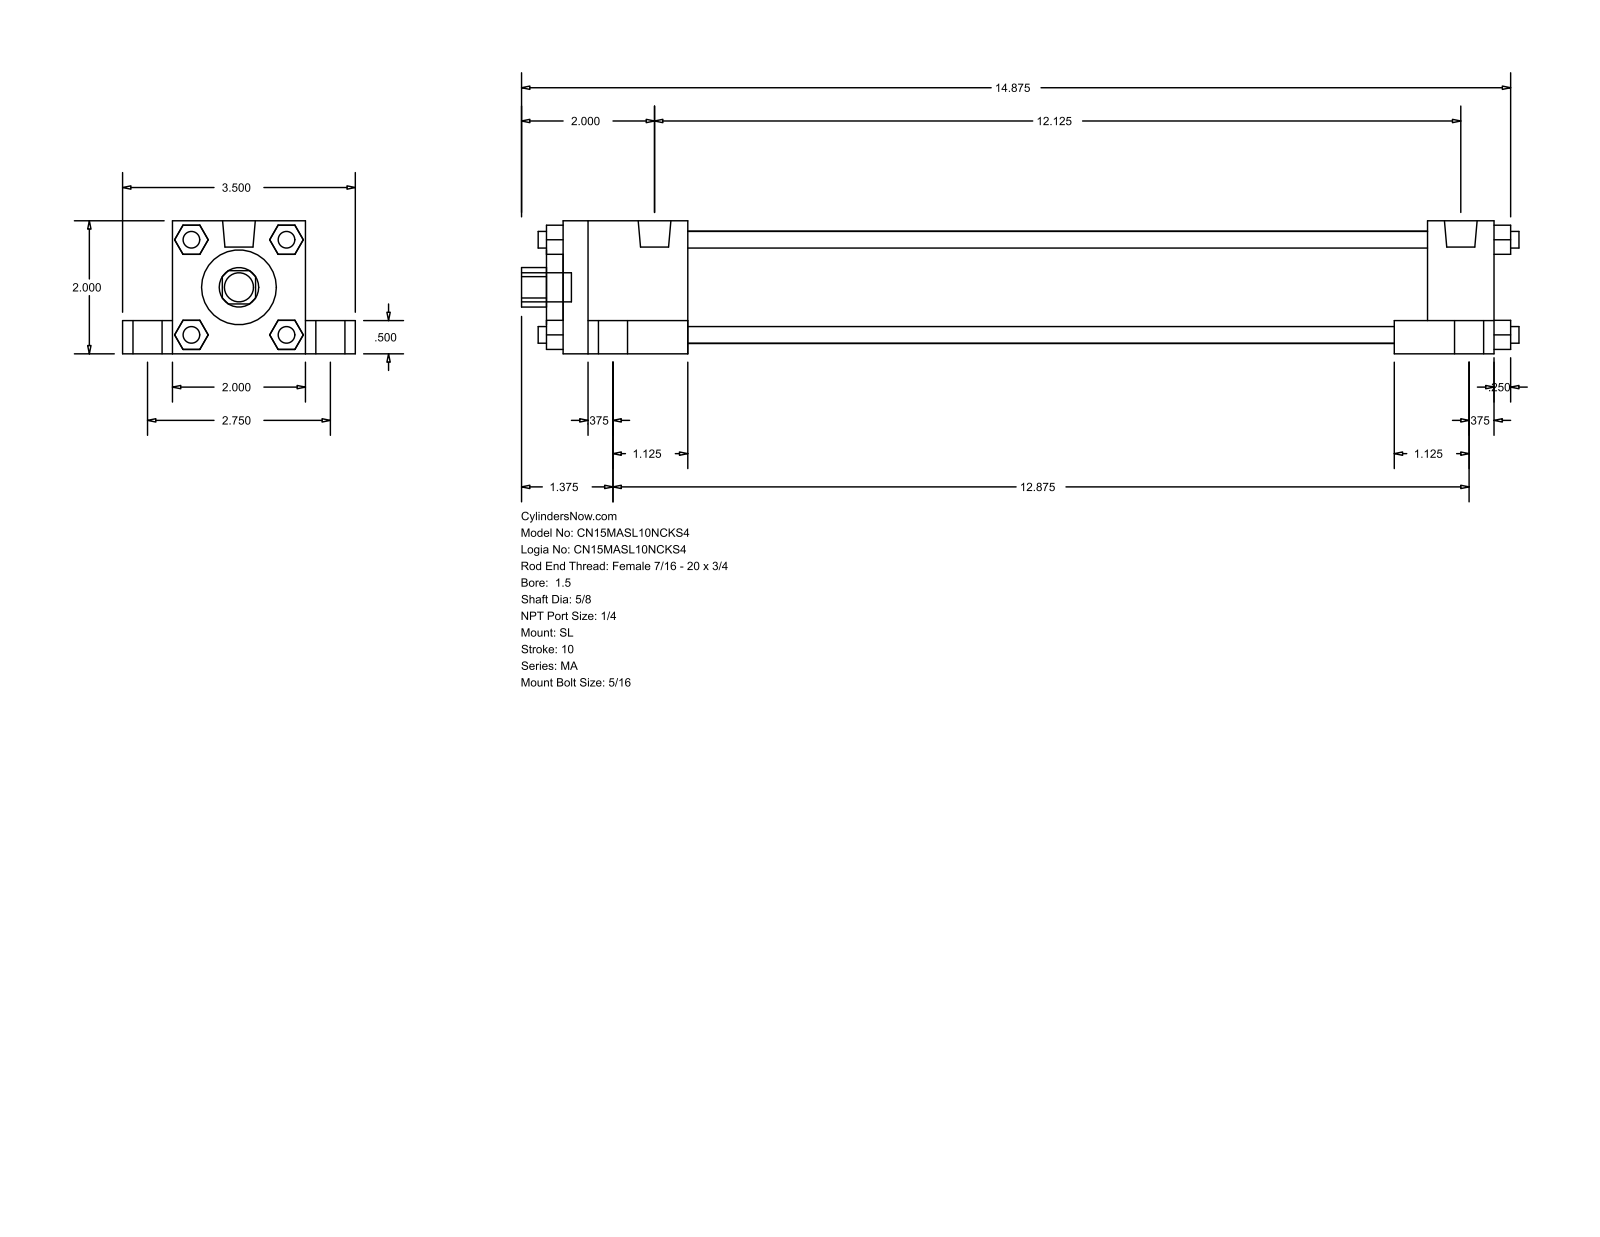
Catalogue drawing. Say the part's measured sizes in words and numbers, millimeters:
The part is named "MA_SL__0150_0.625". Its 3-D file was written by "GSSL Pune (CONFIG_CONTROL_DESIGN)". It is 0 solids with 148 faces: 112 planar, 36 cylindrical and 0 other. Overall it measures 381 by 88.9 by 50.8 millimeters. Round holes: 1 of diameter 15.88, 1 of diameter 28.57, 1 of diameter 42.93. Round bosses or shafts: 5 of diameter 11.11, 4 of diameter 17.46, 4 of diameter 7.94, 4 of diameter 6.35, 2 of diameter 12.49. Partial cylindrical surfaces (rounded edges, fillets, slot ends): 1 of radius 7.54. The main face-to-face distances are 50.8, 19.05, 38.1, 12.7, 355.6, 69.85, 282.57, 9.52, 330.19, 25.41.
